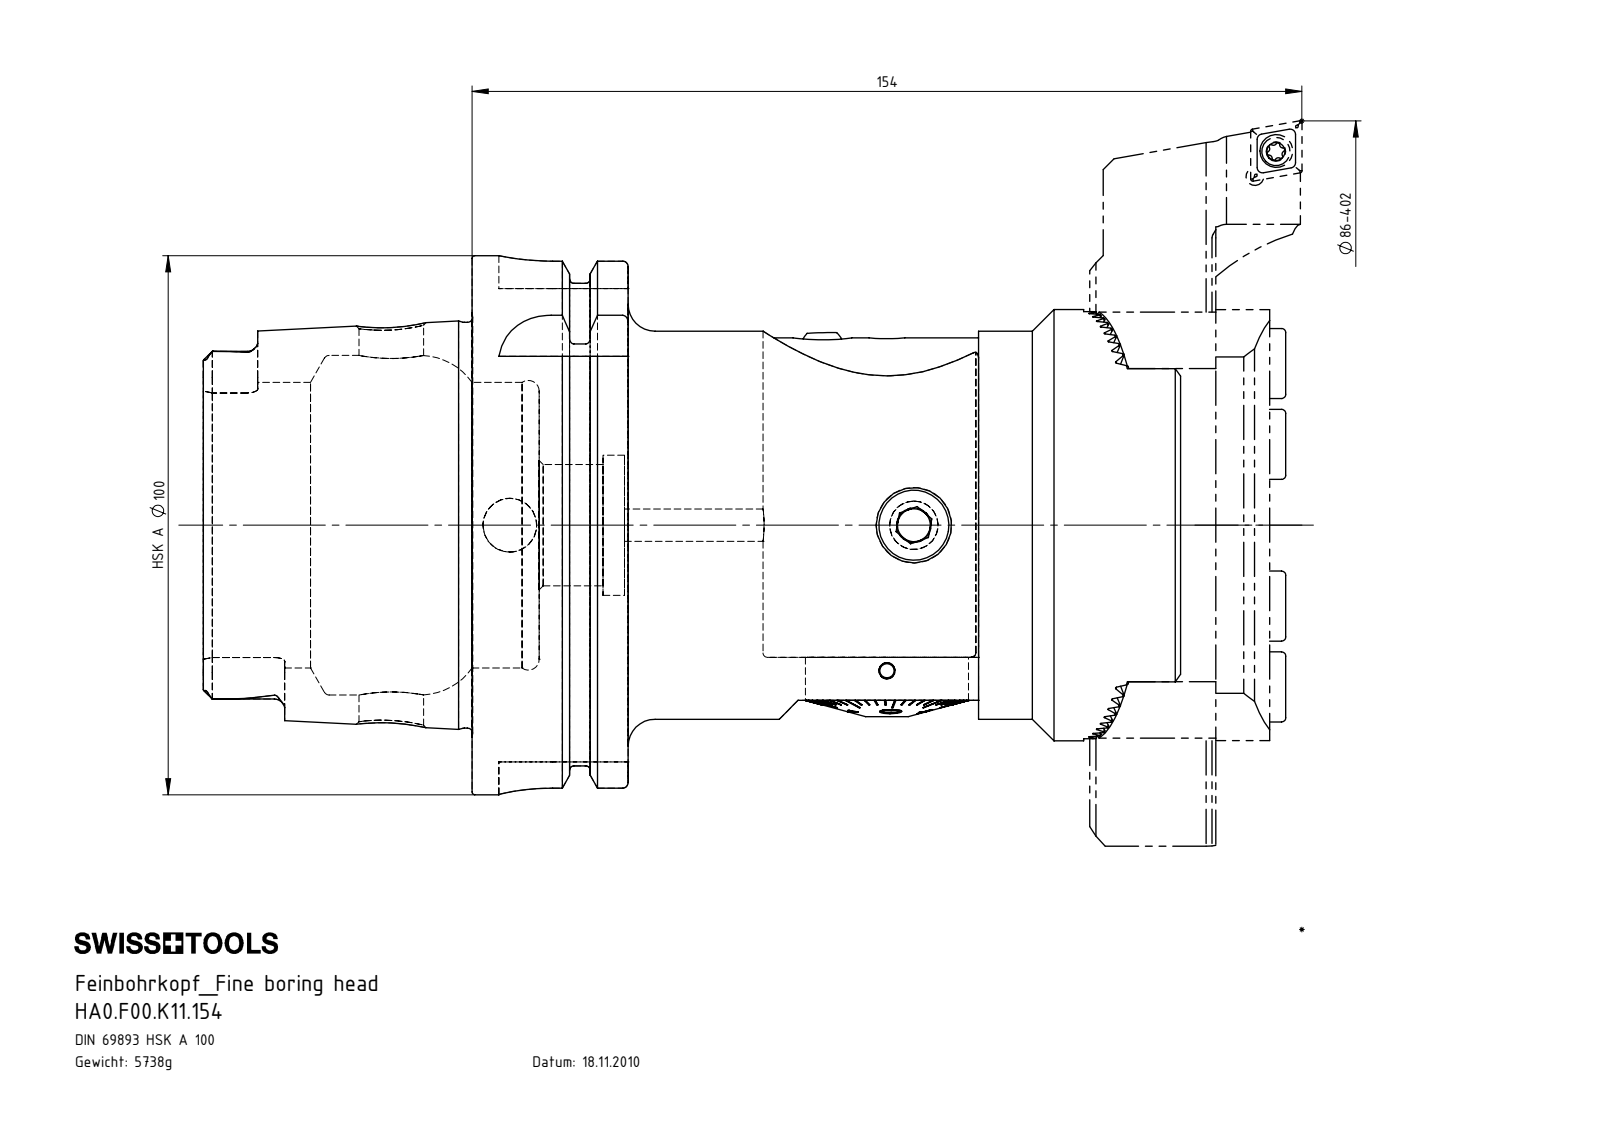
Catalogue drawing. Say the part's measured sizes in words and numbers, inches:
The part is named "HA0.F00.K11.154; F00-ER1.101.045_A_PreviewCfg; KU1-U10.001.010_2; ISO 4762 - M8 x 60 (+8 more)". Its 3-D file was written by "SolidWorks 2017 (AUTOMOTIVE_DESIGN)". It is 23 solids with 1126 faces: 508 planar, 233 cylindrical and 385 other. Overall it measures 7.911 by 3.937 by 3.937 inches. Its volume is 38.43 cubic inches and its surface area 200.6 square inches. Round holes: 5 of diameter 0.197, 5 of diameter 0.394, 4 of diameter 0.268, 4 of diameter 0.276, 4 of diameter 0.413, 2 of diameter 0.118, 2 of diameter 0.236, 1 of diameter 0.039, 1 of diameter 0.124, 1 of diameter 0.13, 1 of diameter 0.256, 1 of diameter 0.305. Round bosses or shafts: 6 of diameter 0.315, 5 of diameter 0.512, 4 of diameter 0.394, 4 of diameter 0.236, 2 of diameter 2.835, 1 of diameter 3.937, 1 of diameter 3.62, 1 of diameter 3.15. Partial cylindrical surfaces (rounded edges, fillets, slot ends): 16 of radius 0.008, 6 of radius 0.075, 4 of radius 0.192, 4 of radius 0.394, 1 of radius 0.404, 1 of radius 0.906, 1 of radius 1.417. The main face-to-face distances are 0.094, 3.701, 0.187, 1.14, 2.561, 0.281, 0.65, 0.49, 3.211, 0.375. The hole center spacings are 0.472, 0.474, 0.591, 0.726, 0.787, 1.309, 1.346, 1.872.
